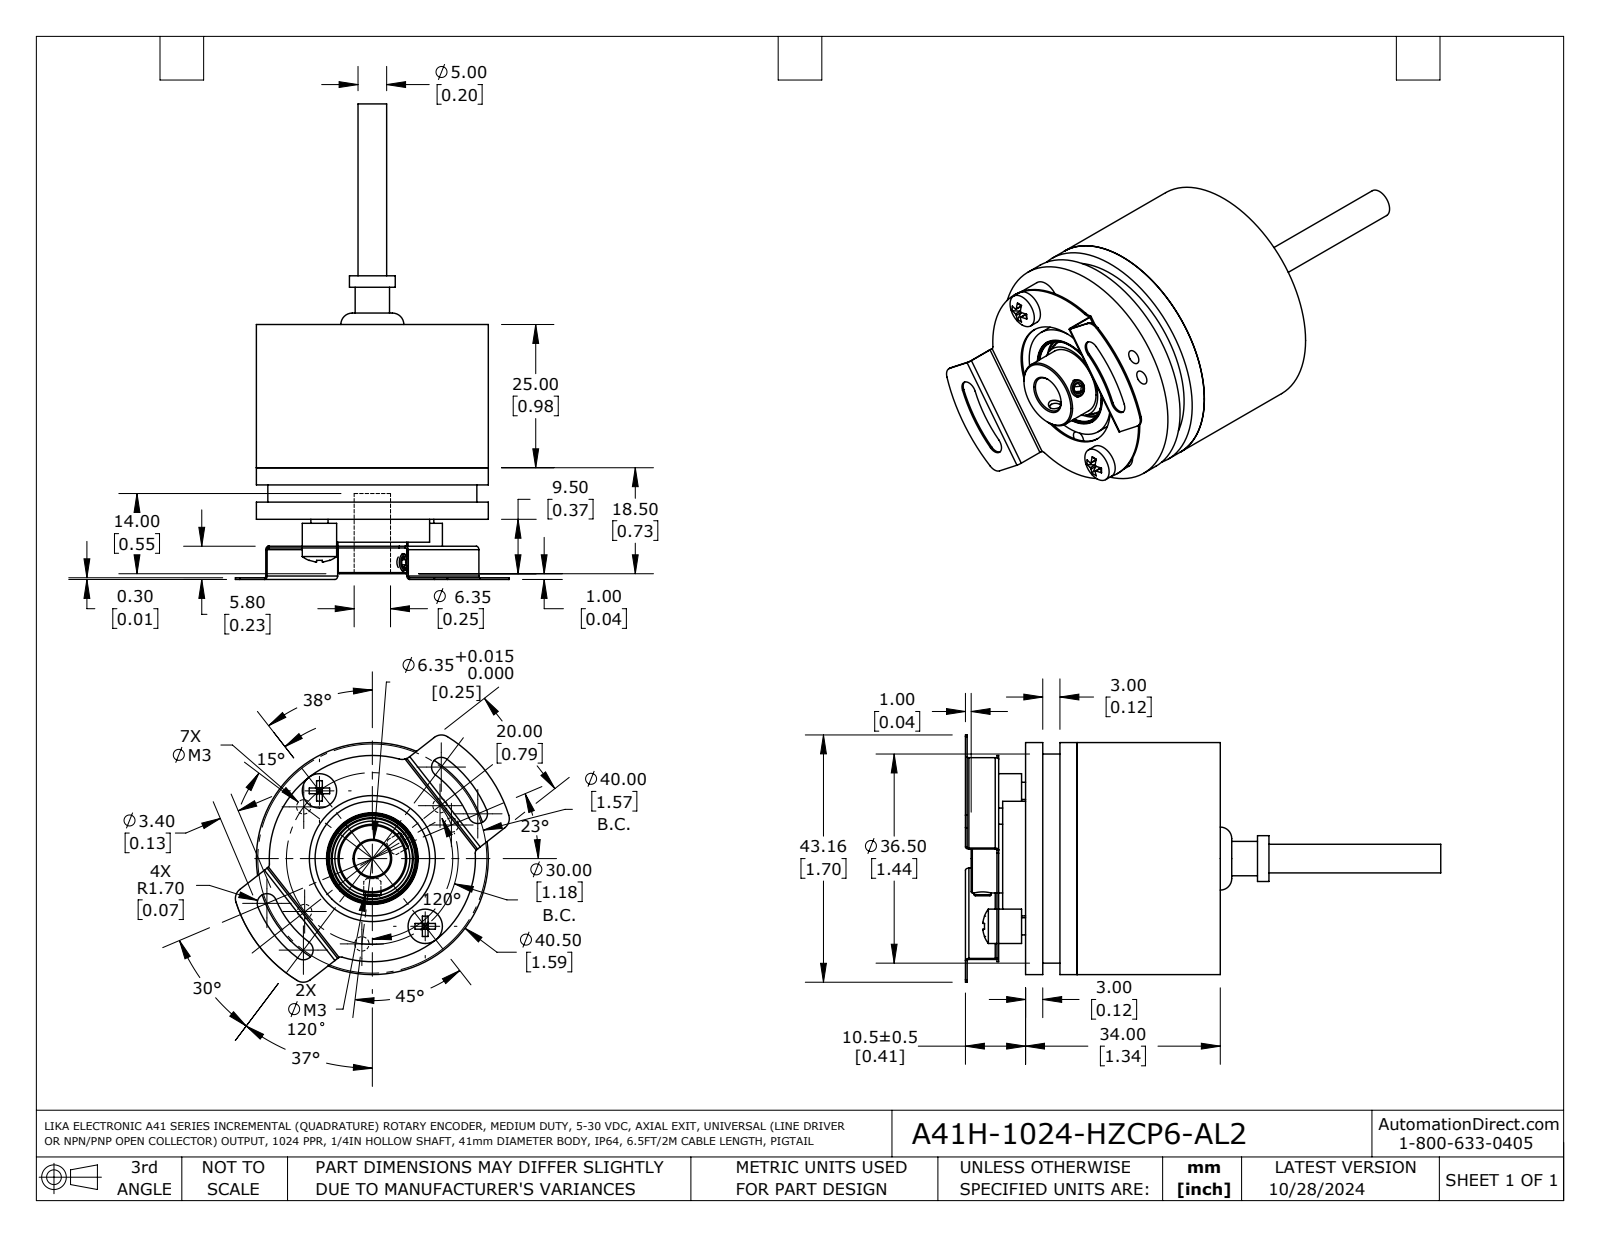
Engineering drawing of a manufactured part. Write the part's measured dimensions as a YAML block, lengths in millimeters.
part_name: "A41H-1024-HZCP6-AL2"
step_written_by: "SolidWorks 2021 (AUTOMOTIVE_DESIGN)"
units: millimeters
bodies: {solids: 15, faces: 465, planar: 139, cylindrical: 186, other: 140}
overall_size: [83, 47.8, 43.2]
volume: 19450
surface_area: 20890
round_holes:
  - {diameter: 2.5, count: 9}
  - {diameter: 1.6, count: 7}
  - {diameter: 4, count: 3}
  - {diameter: 2.2, count: 2}
  - {diameter: 3.2, count: 2}
  - {diameter: 3.5, count: 2}
  - {diameter: 4.3, count: 1}
  - {diameter: 6.4, count: 1}
  - {diameter: 7.5, count: 1}
  - {diameter: 13, count: 1}
  - {diameter: 15.3, count: 1}
  - {diameter: 15.5, count: 1}
round_bosses_or_shafts:
  - {diameter: 3, count: 4}
  - {diameter: 6, count: 3}
  - {diameter: 3.8, count: 2}
  - {diameter: 2, count: 2}
  - {diameter: 40.5, count: 1}
  - {diameter: 38, count: 1}
  - {diameter: 37, count: 1}
  - {diameter: 36.5, count: 1}
partial_cylinders:
  - {radius: 1, count: 14}
  - {radius: 0.2, count: 8}
  - {radius: 2, count: 5}
  - {radius: 0.3, count: 4}
  - {radius: 0.6, count: 4}
  - {radius: 1.7, count: 4}
  - {radius: 0.8, count: 3}
  - {radius: 18, count: 1}
face_to_face_distances: [3, 11, 34, 23, 5, 31, 2, 22, 1, 20]
hole_center_spacings: [15, 17, 21.2, 2.8, 3, 21.3, 24, 26]
